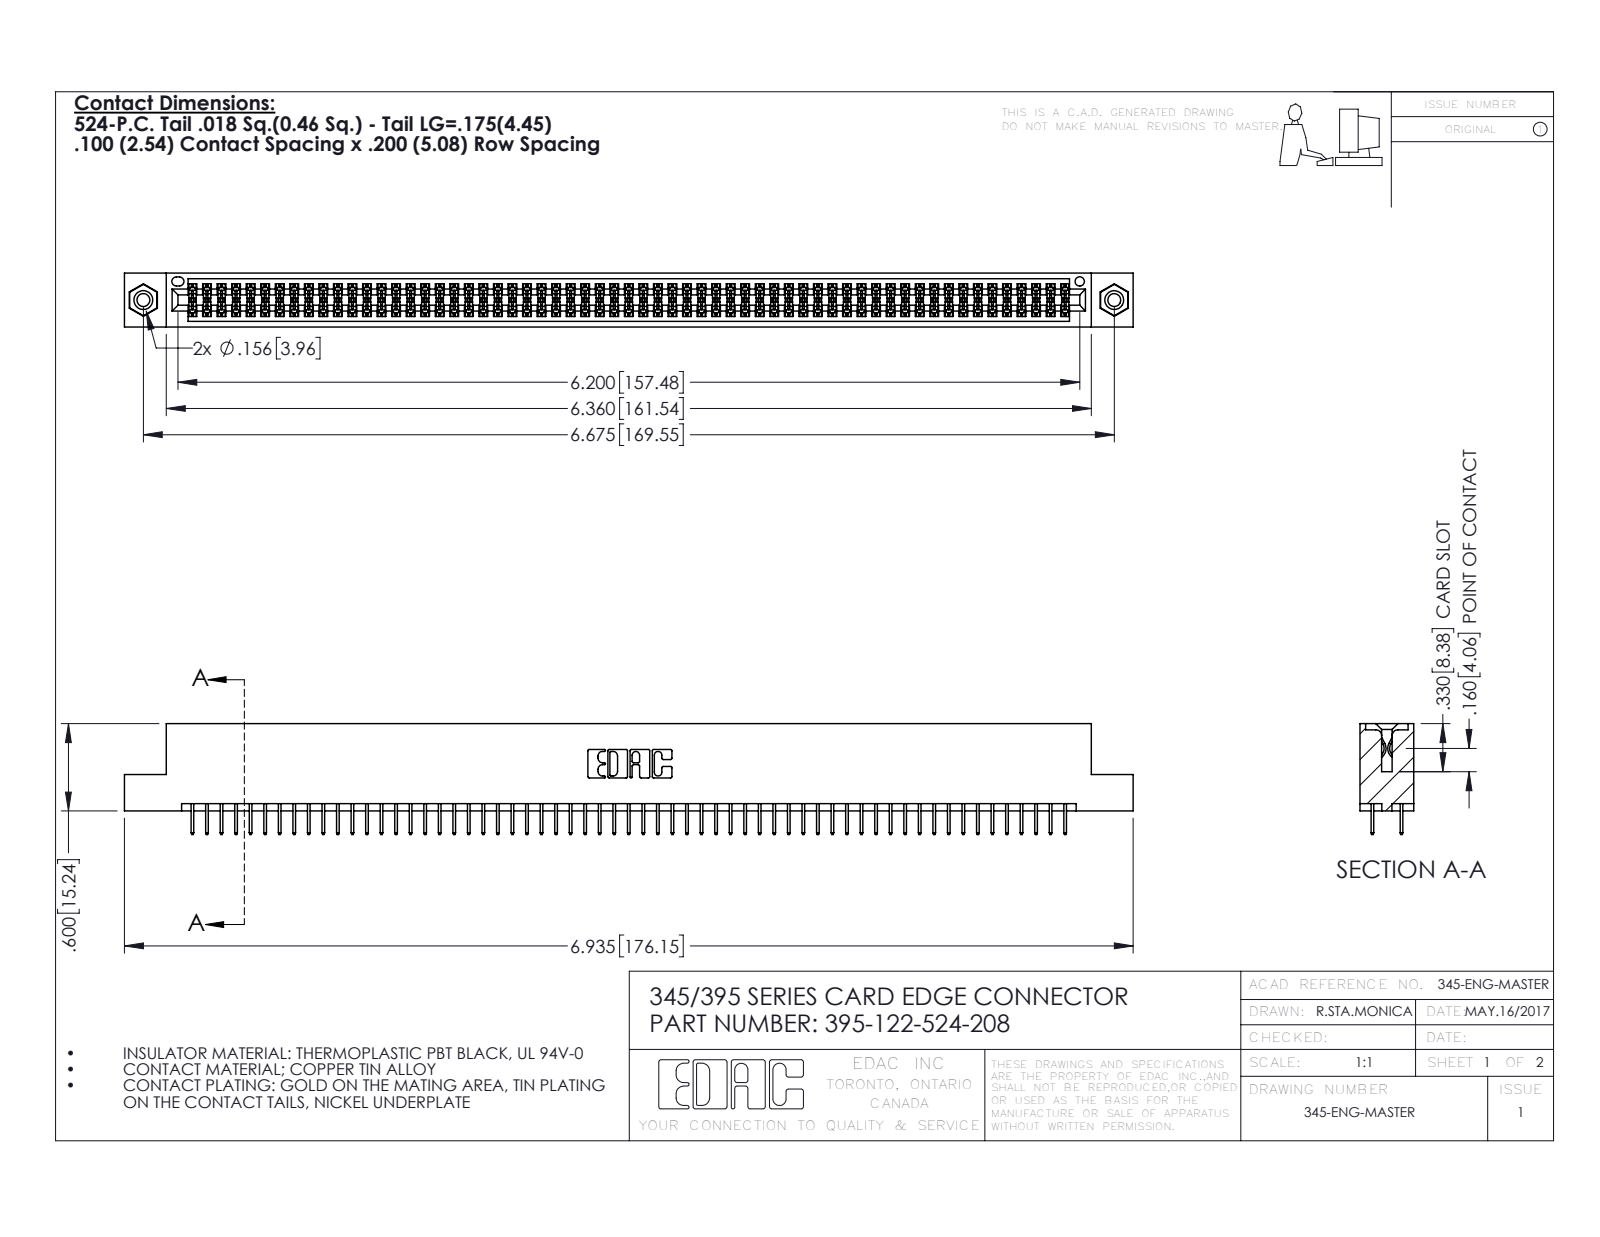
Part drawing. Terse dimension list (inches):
name: 345-250-001_345-250-003-102; 345 Part_Flush Mounting Lugs - 0.156 Dia-TI; 345-292-001_345-293-124; 395-122-524-208
written by: SolidWorks 2016 (CONFIG_CONTROL_DESIGN)
unit: in
bodies: 125 solids, 6774 faces (4870 planar, 1888 cylindrical, 16 other)
size: 6.935 × 0.762 × 0.37
volume: 1.043 in³; area: 39.01 in²
holes: 2× ⌀0.089, 2× ⌀0.125, 2× ⌀0.156, 1× ⌀0.064
bosses: 2× ⌀0.155
rounds: 183× R0.006, 22× R0.01, 6× R0.007, 6× R0.031, 3× R0.026, 2× R0.014, 2× R0.019, 2× R0.022
face distances: 0.072, 0.298, 0.2, 0.37, 0.098, 0.272, 0.025, 0.225, 0.072, 0.175
hole spacings: 0.27, 6.439, 6.675
